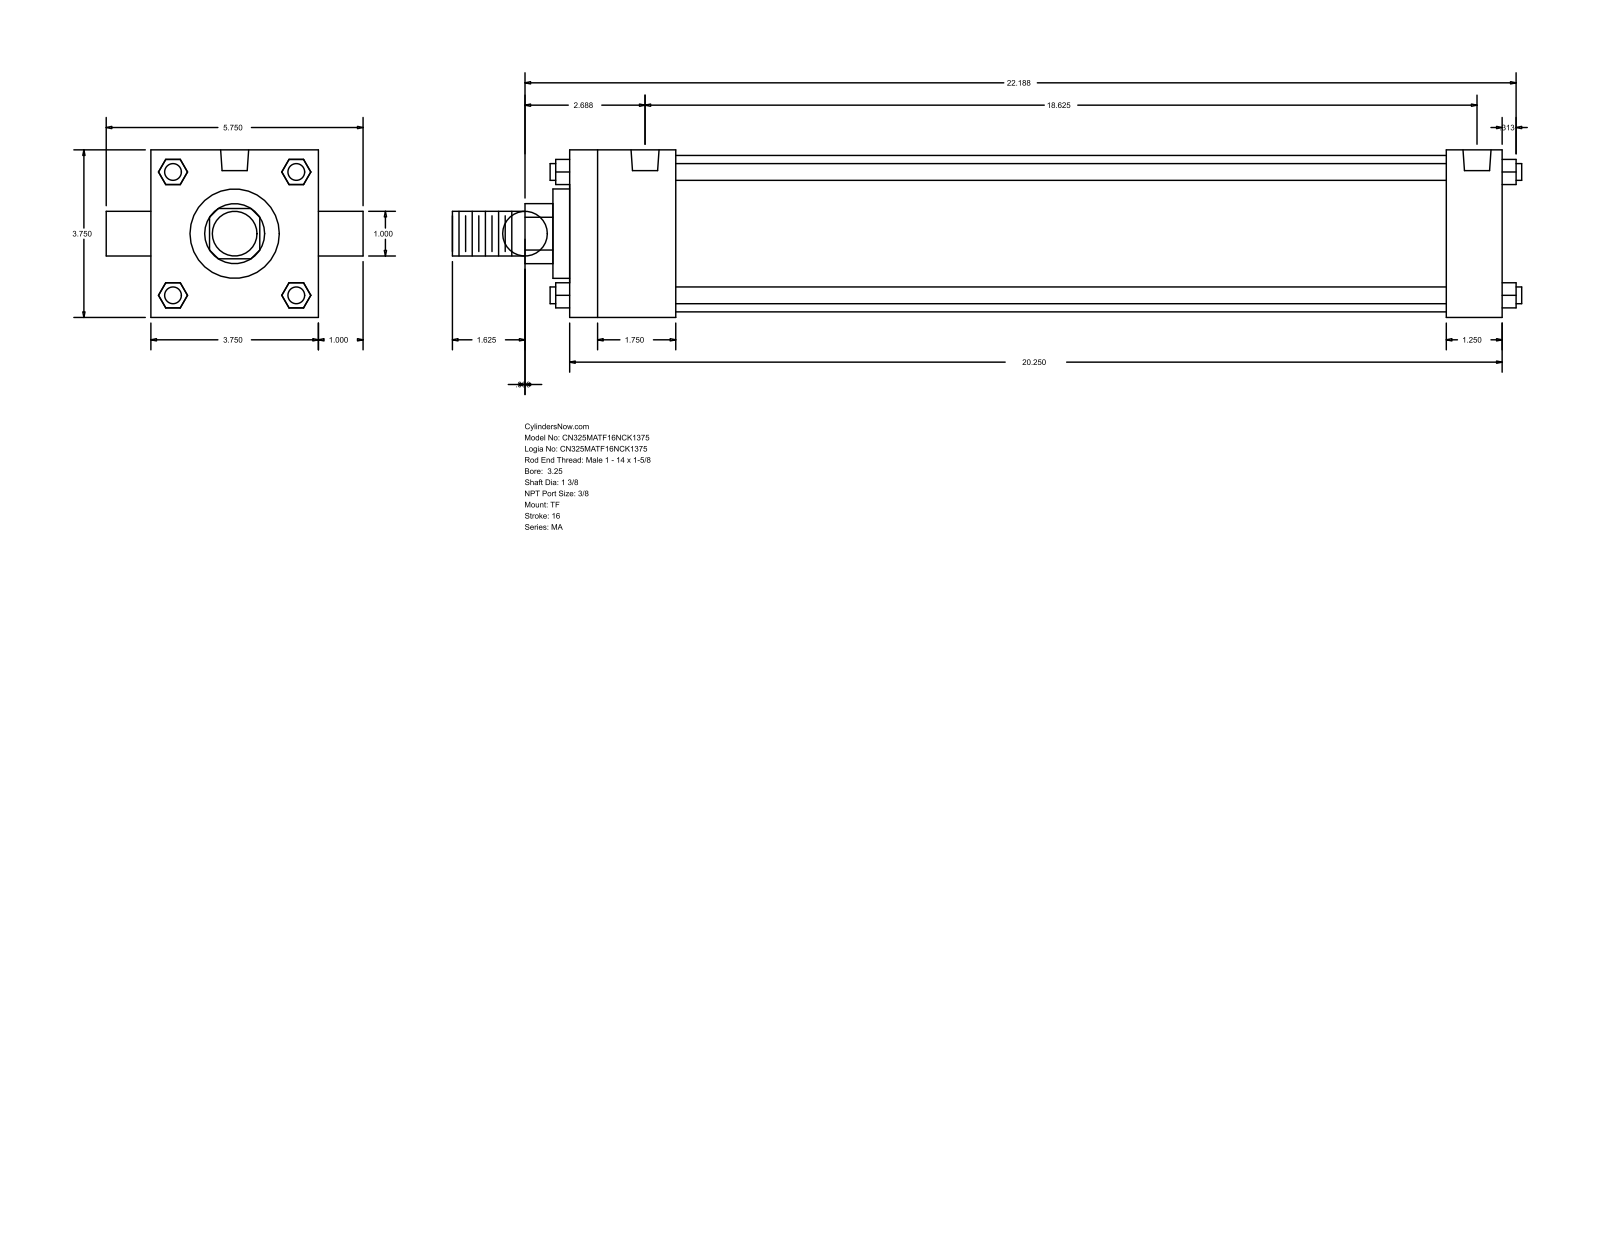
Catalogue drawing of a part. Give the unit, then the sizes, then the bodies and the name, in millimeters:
Units: millimetres
Overall size (bounding box): 608.01 × 146.05 × 95.25
Round holes (diameter × count): ⌀11.11 ×3, ⌀15.93 ×2
Round bosses / shafts (diameter × count): ⌀9.53 ×4, ⌀25.4 ×2, ⌀88.9 ×1, ⌀50.8 ×1, ⌀34.92 ×1
Partial cylindrical surfaces — rounded edges, fillets, slot ends (radius × count): R17.06 ×1
Main face-to-face distances: 95.24, 530.22, 60.32, 498.48, 438.16, 469.9, 31.74, 9.52, 69.84, 508
Hole centre spacings: 4.76, 4.77, 463.55, 468.31, 468.32, 473.08
Bodies: 0 solids, 120 faces (92 planar, 28 cylindrical, 0 other)
Part name (STEP PRODUCT): MA_TF__0325_1.375
STEP written by: GSSL Pune (CONFIG_CONTROL_DESIGN)
